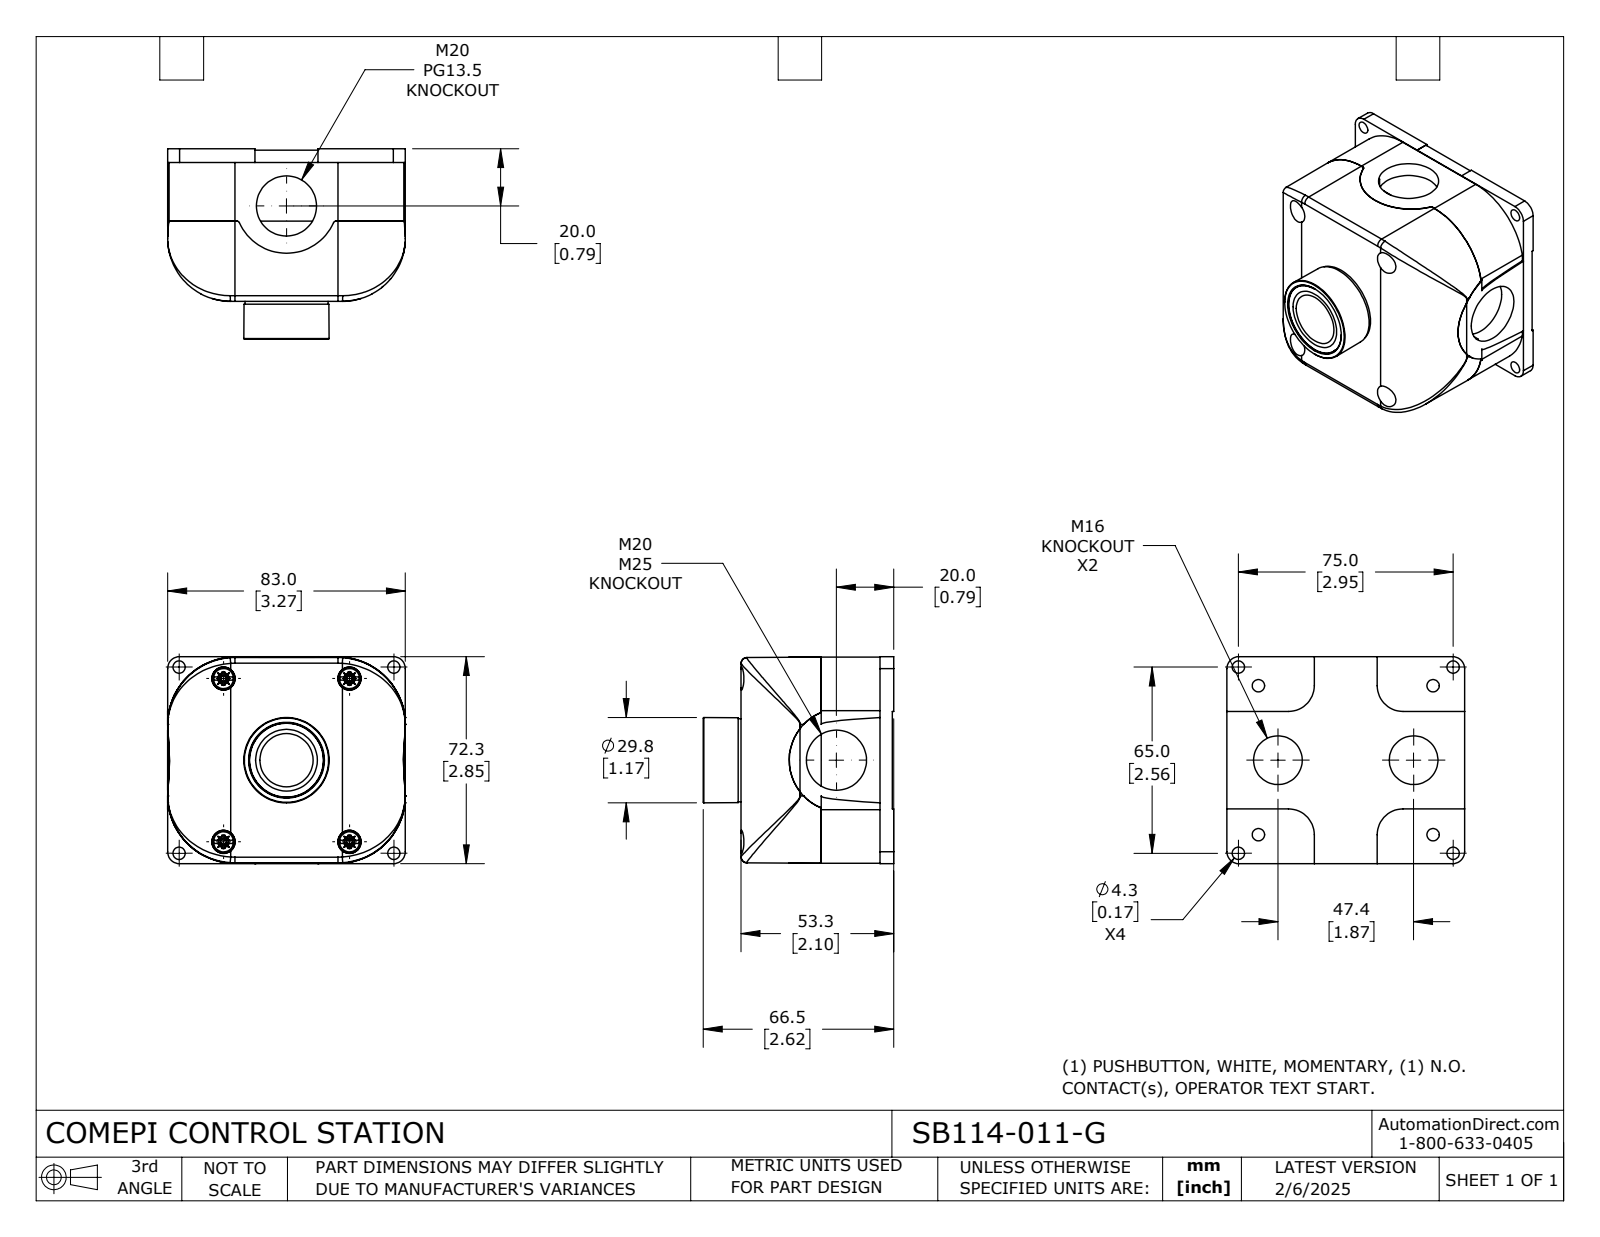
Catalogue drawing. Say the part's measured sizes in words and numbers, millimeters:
The part is named "SB114-011-G". Its 3-D file was written by "SolidWorks 2024 (CONFIG_CONTROL_DESIGN)". It is 4 solids with 548 faces: 300 planar, 144 cylindrical and 104 other. Overall it measures 83 by 72.3 by 66.5 millimeters. Its volume is 209 800 cubic millimeters and its surface area 57 630 square millimeters. Round holes: 8 of diameter 4.3, 4 of diameter 8.2, 2 of diameter 17, 2 of diameter 21, 1 of diameter 13.5, 1 of diameter 18.1, 1 of diameter 21.7. Round bosses or shafts: 4 of diameter 7, 1 of diameter 29, 1 of diameter 25.8, 1 of diameter 19, 1 of diameter 18.5, 1 of diameter 16, 1 of diameter 15.6, 1 of diameter 15.5. Partial cylindrical surfaces (rounded edges, fillets, slot ends): 4 of radius 0.9, 4 of radius 2, 4 of radius 9, 4 of radius 9.7, 4 of radius 23.5, 2 of radius 0.2, 2 of radius 0.3, 2 of radius 18. The main face-to-face distances are 24.8, 2.5, 22.3, 52.8, 50.3, 28, 3, 53.3, 0.5, 25.3. The hole center spacings are 9.6, 26.9, 35.3, 40.1, 49.6, 58.9, 60.1, 68.3.
